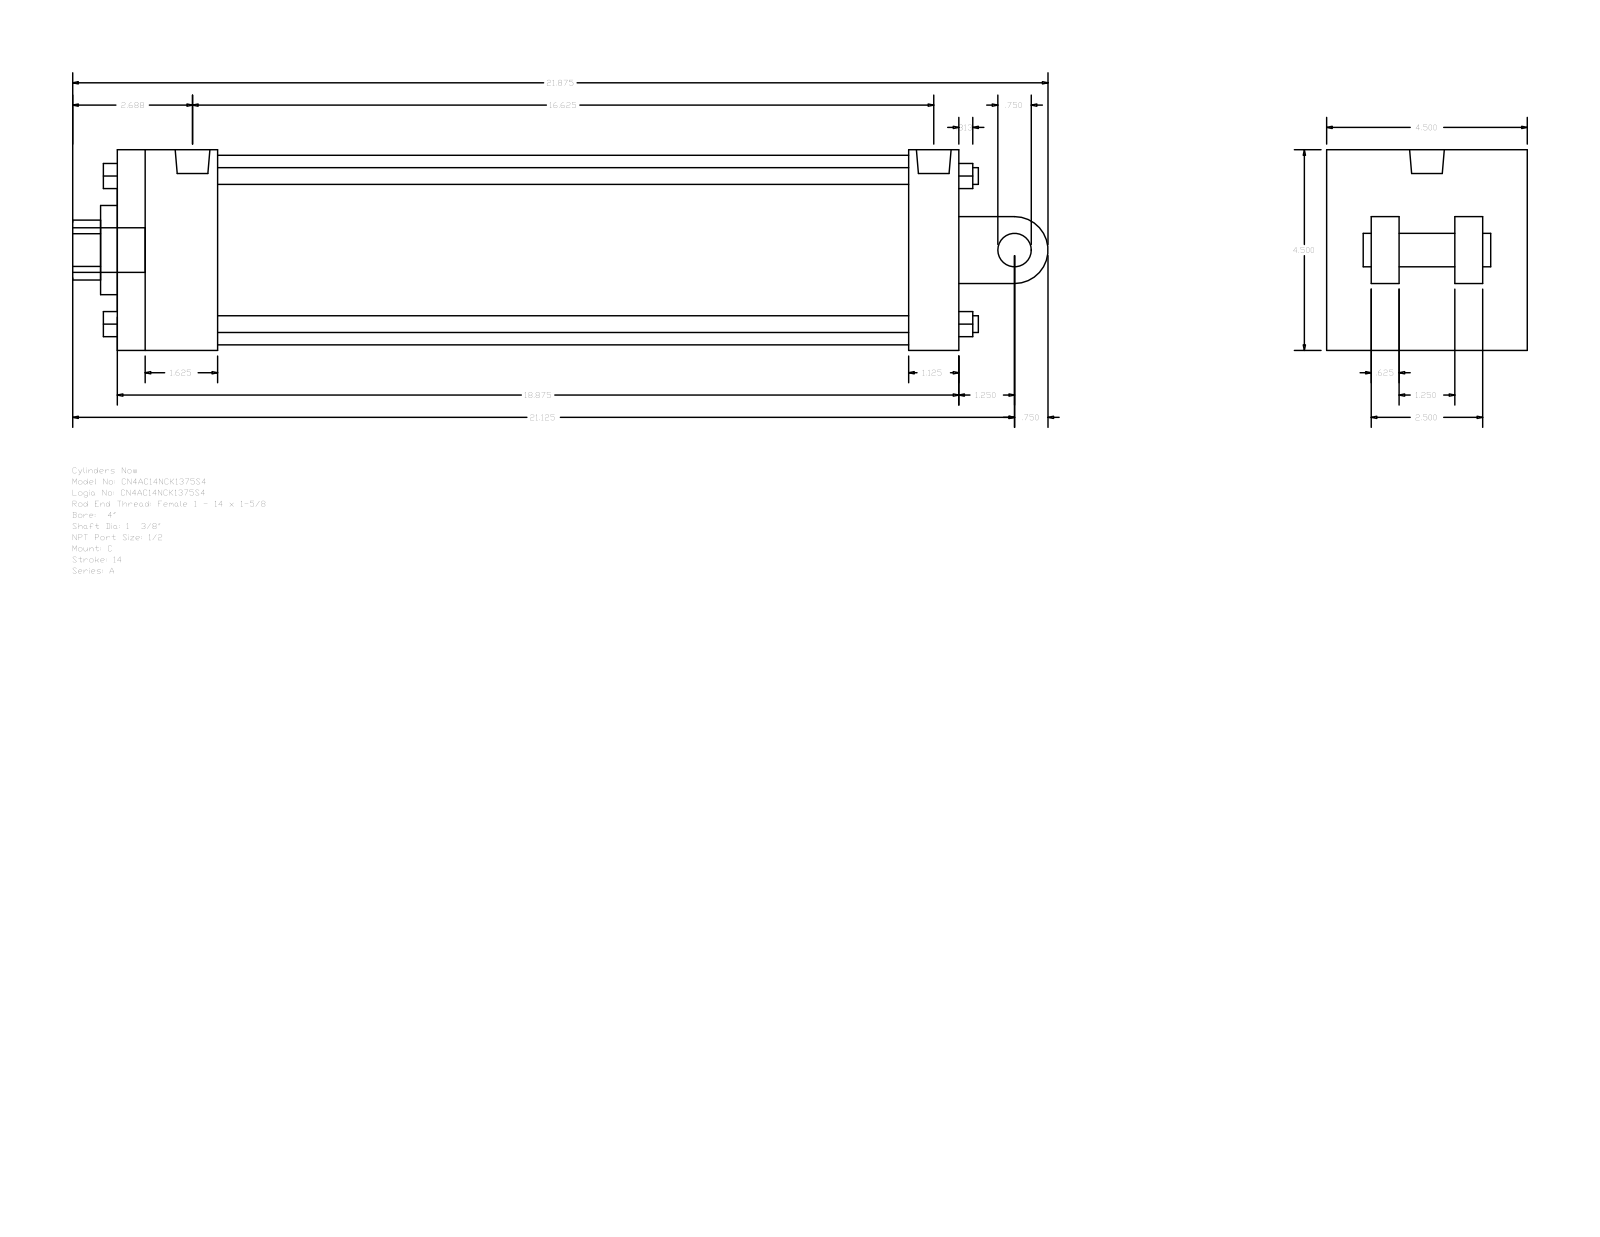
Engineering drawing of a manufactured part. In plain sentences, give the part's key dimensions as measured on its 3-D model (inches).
The part is named "A_C__0400_1.375". Its 3-D file was written by "GSSL Pune (CONFIG_CONTROL_DESIGN)". It is 0 solids with 135 faces: 102 planar, 33 cylindrical and 0 other. Overall it measures 21.875 by 4.5 by 4.5 inches. Round holes: 2 of diameter 0.344, 1 of diameter 0.778, 1 of diameter 1.375, 1 of diameter 2, 1 of diameter 4.25. Round bosses or shafts: 4 of diameter 0.375, 2 of diameter 0.344, 1 of diameter 1, 1 of diameter 0.778, 1 of diameter 0.75. Partial cylindrical surfaces (rounded edges, fillets, slot ends): 1 of radius 0.672, 1 of radius 0.75. The main face-to-face distances are 4.5, 18.875, 2.875, 1.125, 17.75, 2.25, 15.5, 16.625, 0.625, 1.625. The hole center spacings are 0.125.
